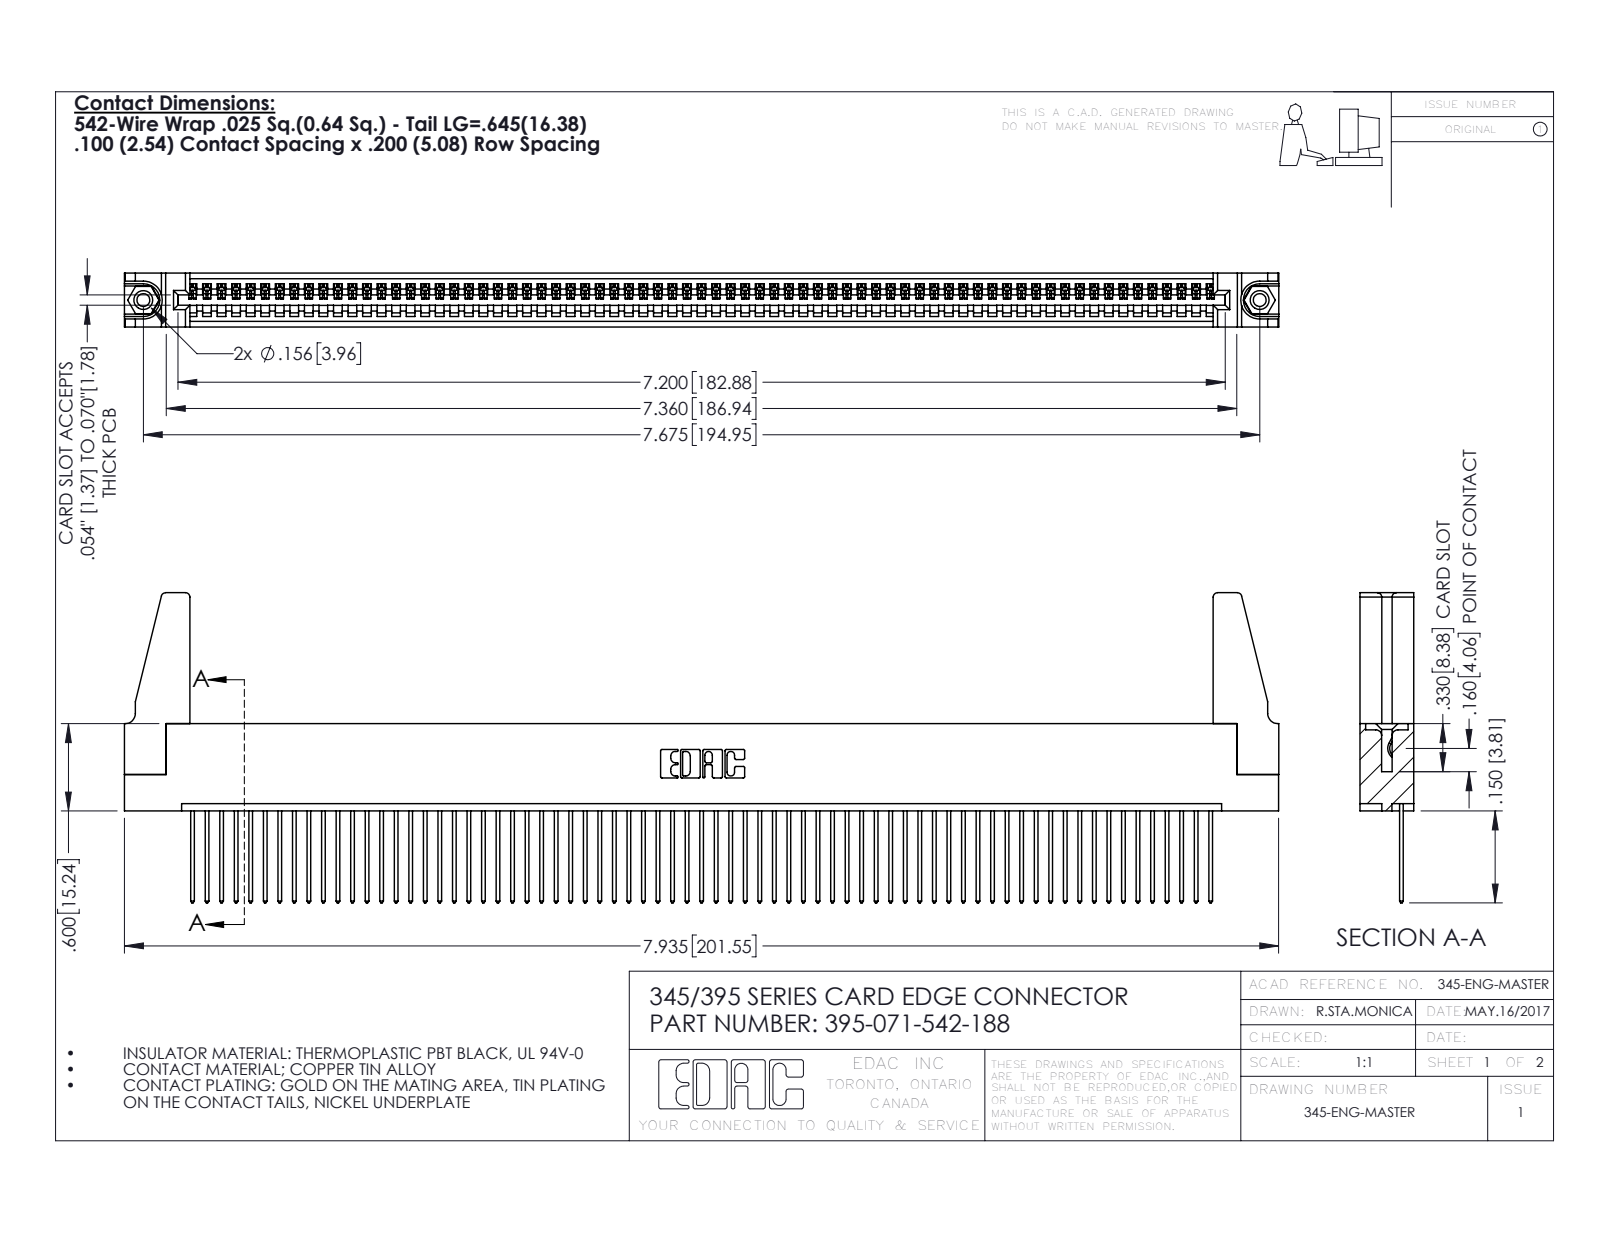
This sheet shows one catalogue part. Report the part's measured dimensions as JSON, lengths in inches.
{"part_name": "345-220-078_345-220-088; 345-250-001_345-250-001-102; 395-071-542-188; 345-292-001_345-293-142 (+1 more)", "step_written_by": "SolidWorks 2016 (CONFIG_CONTROL_DESIGN)", "units": "inches", "bodies": {"solids": 76, "faces": 4368, "planar": 2992, "cylindrical": 1360, "other": 16}, "overall_size": [7.936, 2.132, 0.37], "volume_in3": 1.391, "surface_area_in2": 47.26, "round_holes": [[0.089, 2], [0.125, 2], [0.156, 2], [0.064, 1]], "round_bosses_or_shafts": [[0.155, 2]], "partial_cylinders_radius": [[0.006, 142], [0.01, 142], [0.01, 22], [0.03, 8], [0.007, 6], [0.031, 6], [0.026, 3], [0.031, 2]], "face_to_face_distances": [0.072, 0.298, 0.37, 0.098, 0.272, 0.025, 0.2, 0.225, 0.149, 0.072], "hole_center_spacings": [0.27, 7.439, 7.675]}
